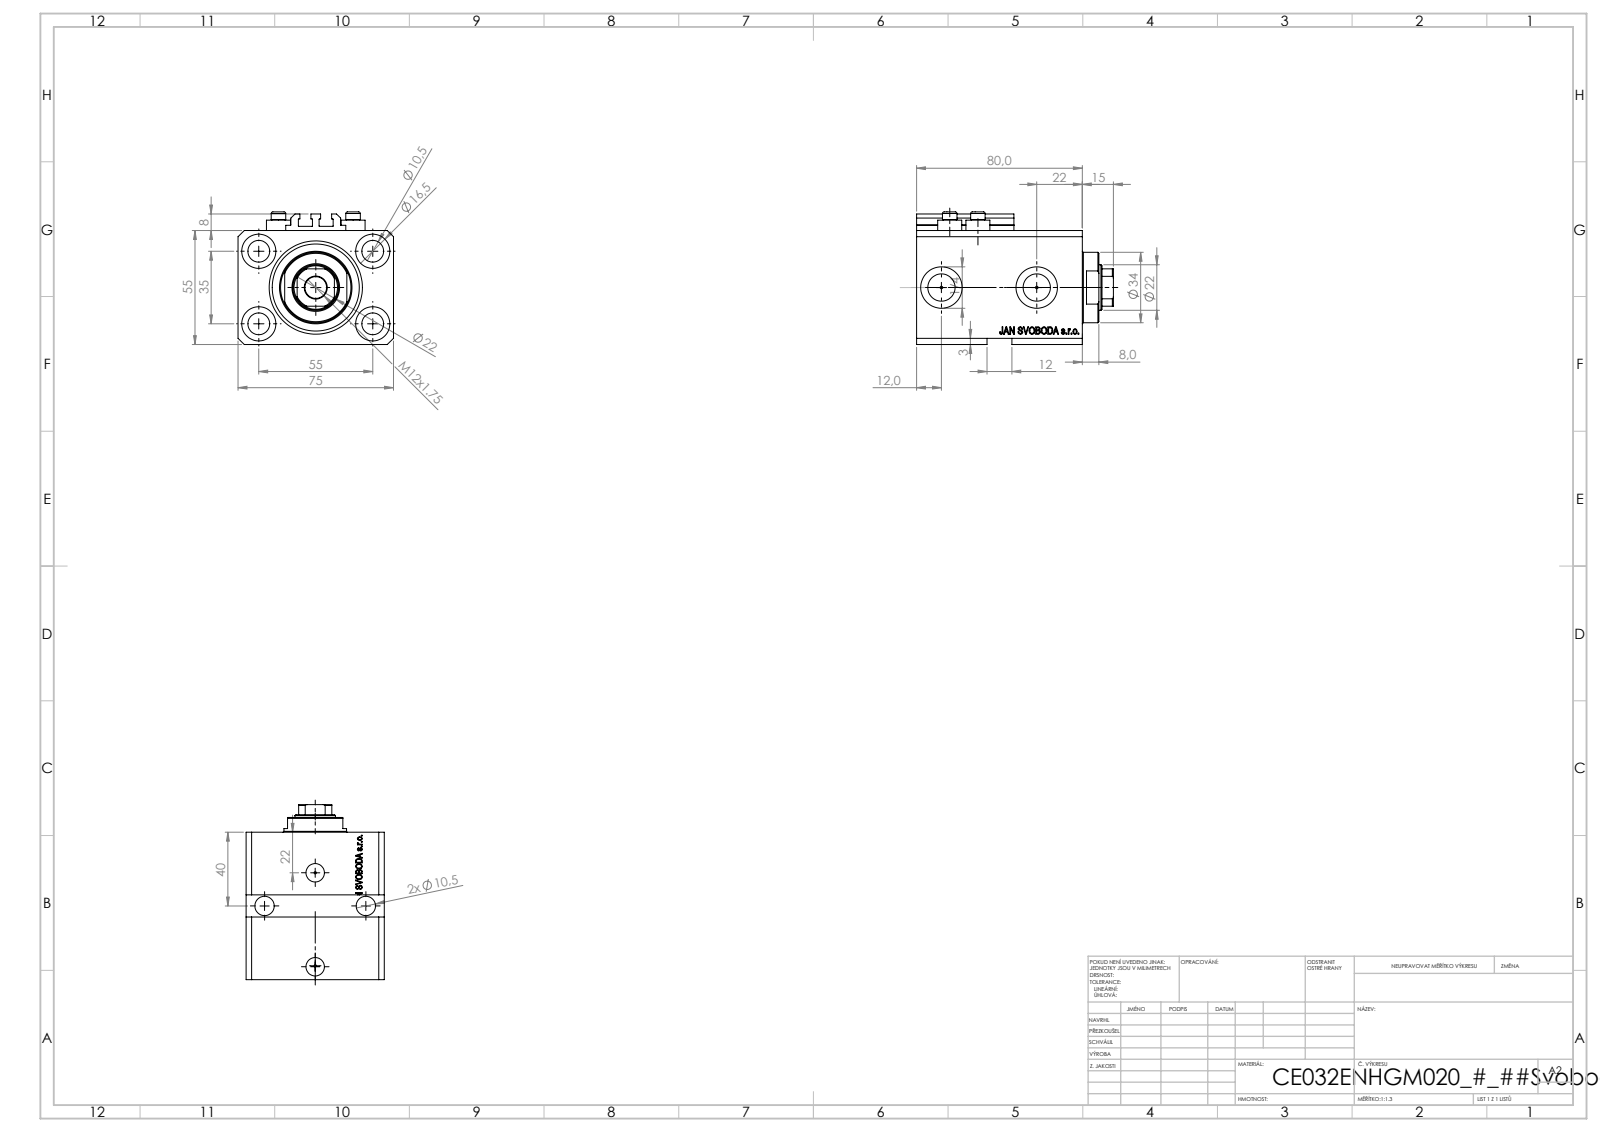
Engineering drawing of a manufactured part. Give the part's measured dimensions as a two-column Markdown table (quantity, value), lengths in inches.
| quantity | value |
| --- | --- |
| part name | V250CE_VC_E; ALLEN BOLT V250CE; V250CE_E_Body; V250CE_C_VCP |
| STEP written by | SolidWorks 2019 (CONFIG_CONTROL_DESIGN) |
| units | inches |
| bodies | 8 solids, 1064 faces (514 planar, 126 cylindrical, 424 other) |
| overall size | 3.74 × 2.953 × 2.52 |
| volume | 17.32 in³ |
| surface area | 115.4 in² |
| round holes (diameter × count) | 0.413 × 7, 0.049 × 4, 0.157 × 4, 0.65 × 4, 0.394 × 2, 0.518 × 2, 0.787 × 2, 0.866 × 1, 1.26 × 1, 1.772 × 1 |
| round bosses / shafts (diameter × count) | 0.457 × 4, 0.276 × 4, 1.339 × 1 |
| partial cylindrical surfaces (radius × count) | 0.008 × 10, 0.413 × 1 |
| main face-to-face distances | 2.165, 2.953, 0.591, 3.15, 2.559, 0.118, 2.169, 0.39, 2.76, 2.126 |
| hole center spacings | 1.283, 2.165, 0.535, 0.555, 0.783, 0.792, 1.016, 1.121 |
